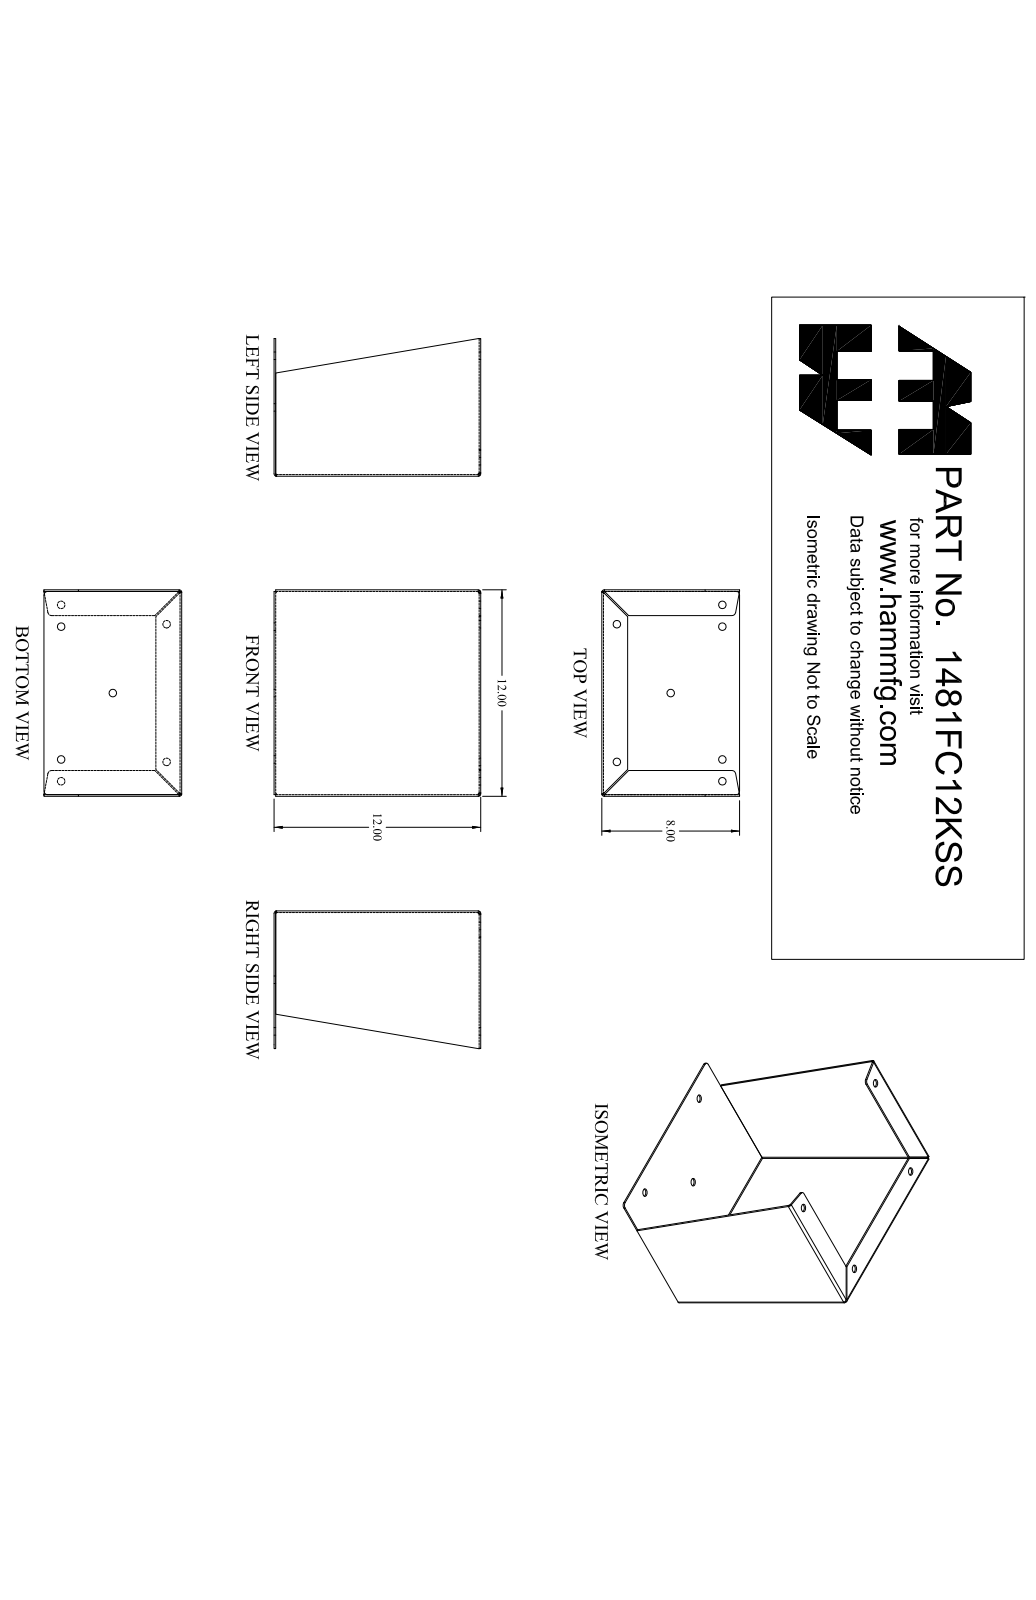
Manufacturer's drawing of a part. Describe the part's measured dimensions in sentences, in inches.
The part is named "1481FC12KSS_Default". Its 3-D file was written by "SolidWorks 2019 (CONFIG_CONTROL_DESIGN)". It is 1 solid with 78 faces: 42 planar, 30 cylindrical and 6 other. Overall it measures 12 by 12 by 8 inches. Its volume is 41.08 cubic inches and its surface area 875 square inches. Round holes: 7 of diameter 0.437. Partial cylindrical surfaces (rounded edges, fillets, slot ends): 6 of radius 0.048, 6 of radius 0.143, 4 of radius 0.22. The main face-to-face distances are 0.095, 11.905, 12, 0.095, 11.81, 11.81, 11.905, 1.405, 1.5, 10.5. The hole center spacings are 4.888, 5.076, 6.126, 6.227, 9.964, 1.266, 1.266, 5.939.
